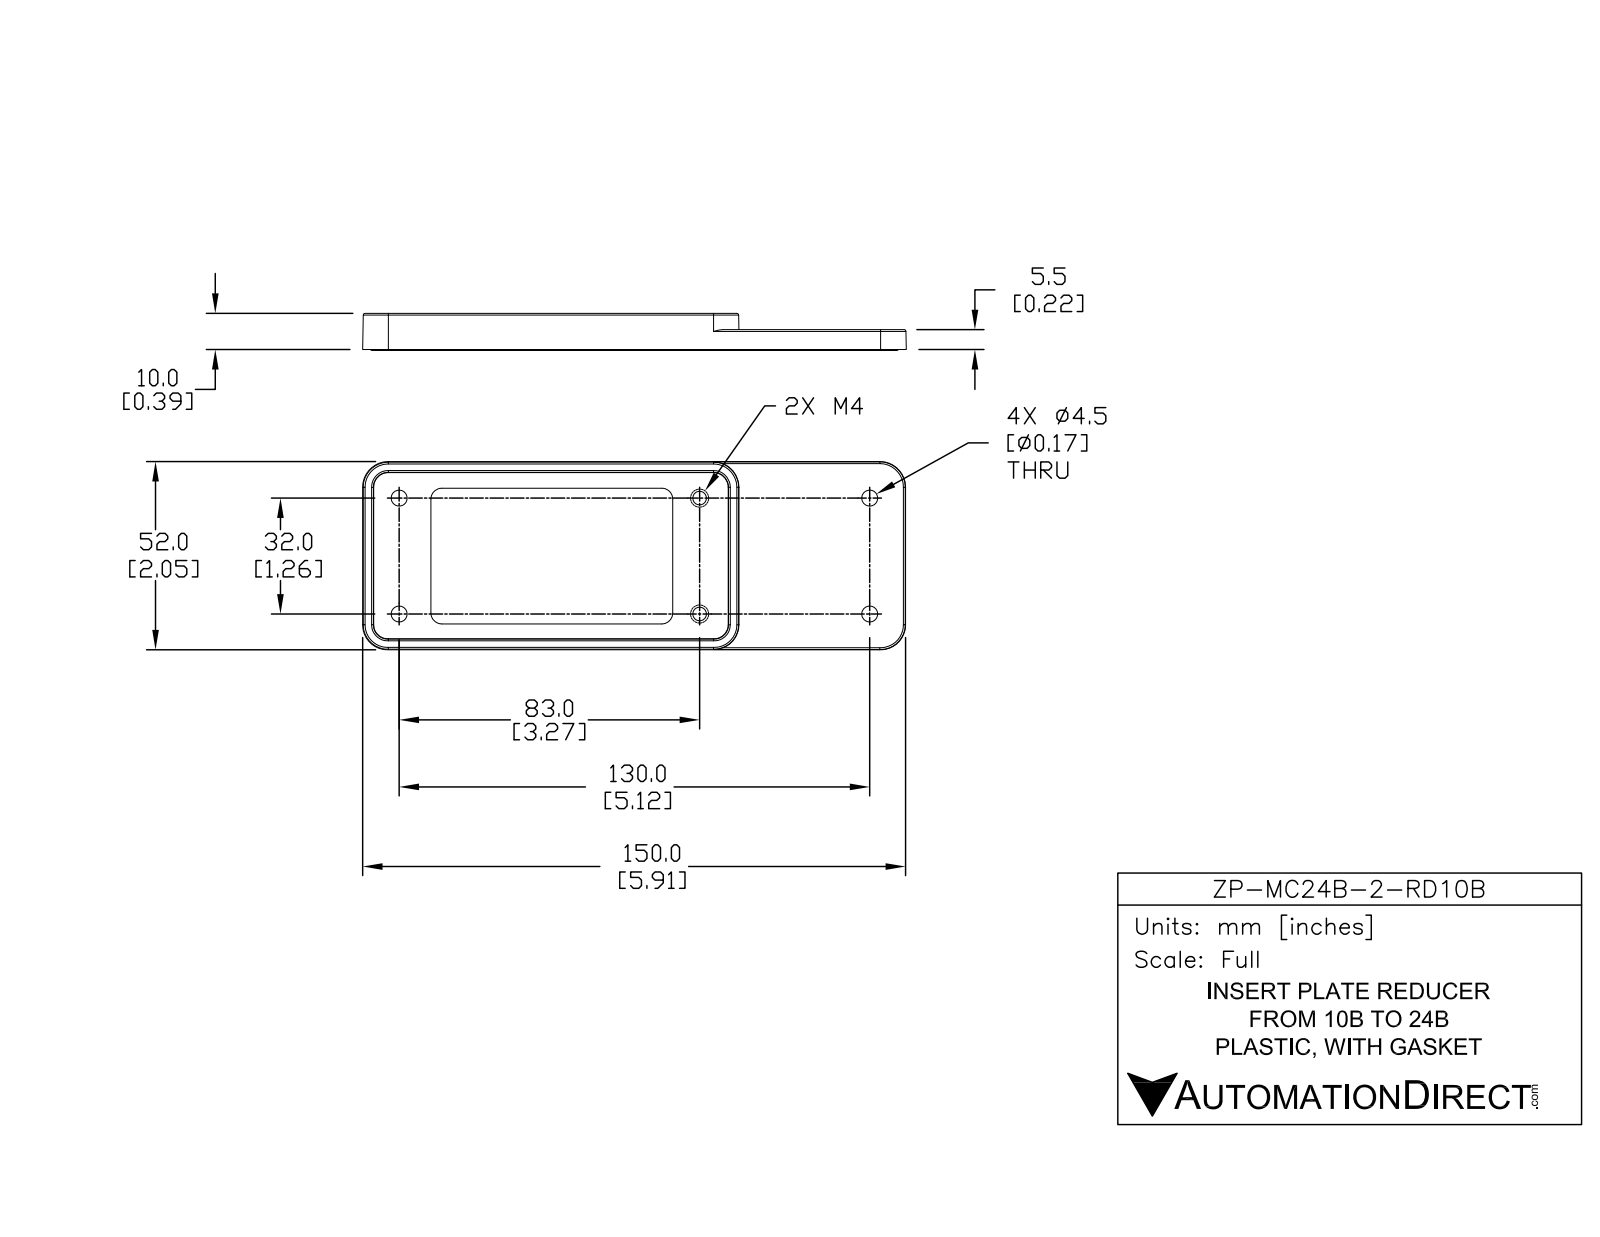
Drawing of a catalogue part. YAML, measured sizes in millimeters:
part_name: "ZP-MC24B-2-RD10B"
step_written_by: "SolidWorks 2014 (AUTOMOTIVE_DESIGN)"
units: millimeters
bodies: {solids: 1, faces: 161, planar: 61, cylindrical: 72, other: 28}
overall_size: [150.19, 52.19, 10.25]
volume: 26718
surface_area: 17687
round_holes:
  - {diameter: 4.4, count: 4}
  - {diameter: 3.75, count: 2}
partial_cylinders:
  - {radius: 0.5, count: 27}
  - {radius: 3, count: 4}
  - {radius: 4.2, count: 4}
  - {radius: 1.5, count: 3}
  - {radius: 1.5, count: 2}
  - {radius: 1.52, count: 2}
  - {radius: 5.5, count: 2}
  - {radius: 1.52, count: 1}
face_to_face_distances: [3, 5.5, 2.5, 3.25, 5.75, 49.05, 10.25, 10, 7, 4.5]
hole_center_spacings: [32, 47, 56.86, 83, 88.96, 130, 133.88]
